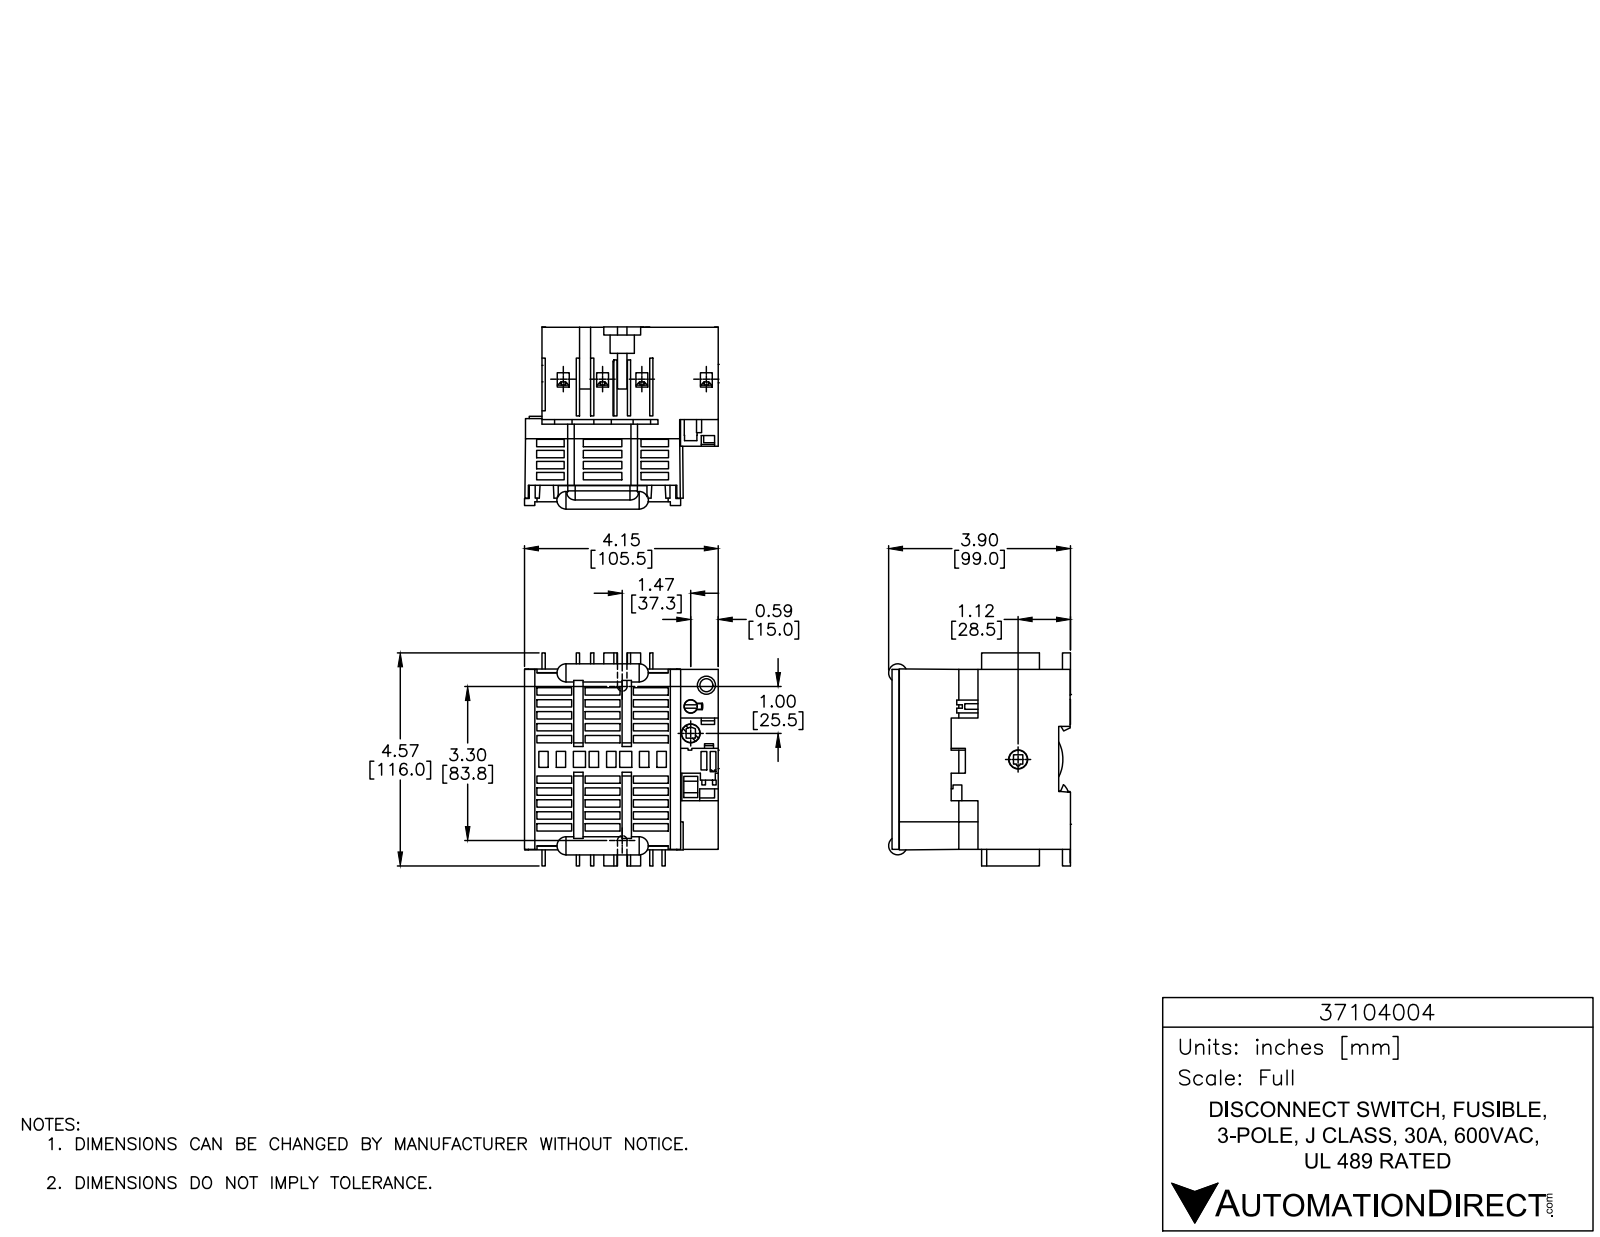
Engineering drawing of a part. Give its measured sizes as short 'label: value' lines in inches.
name: 37104004
written by: SolidWorks 2015 (AUTOMOTIVE_DESIGN)
unit: in
bodies: 3 solids, 2210 faces (1893 planar, 272 cylindrical, 45 other)
size: 4.567 × 4.154 × 3.906
volume: 32.19 in³; area: 212.9 in²
holes: 10× ⌀0.276, 4× ⌀0.146, 3× ⌀0.087, 1× ⌀0.165, 1× ⌀0.287, 1× ⌀0.362, 1× ⌀0.386, 1× ⌀0.402, 1× ⌀0.409
bosses: 4× ⌀0.374, 2× ⌀0.394, 1× ⌀0.354, 1× ⌀0.276
rounds: 27× R0.02, 20× R0.01, 12× R0.039, 12× R0.197, 12× R0.276, 8× R0.051, 8× R0.059, 5× R0.118
face distances: 0.071, 0.079, 3.78, 1.274, 2.387, 3.661, 3.858, 1.764, 3.74, 1.353
hole spacings: 0.843, 0.428, 3.277, 3.287, 1.685, 3.177, 0.375, 0.793
